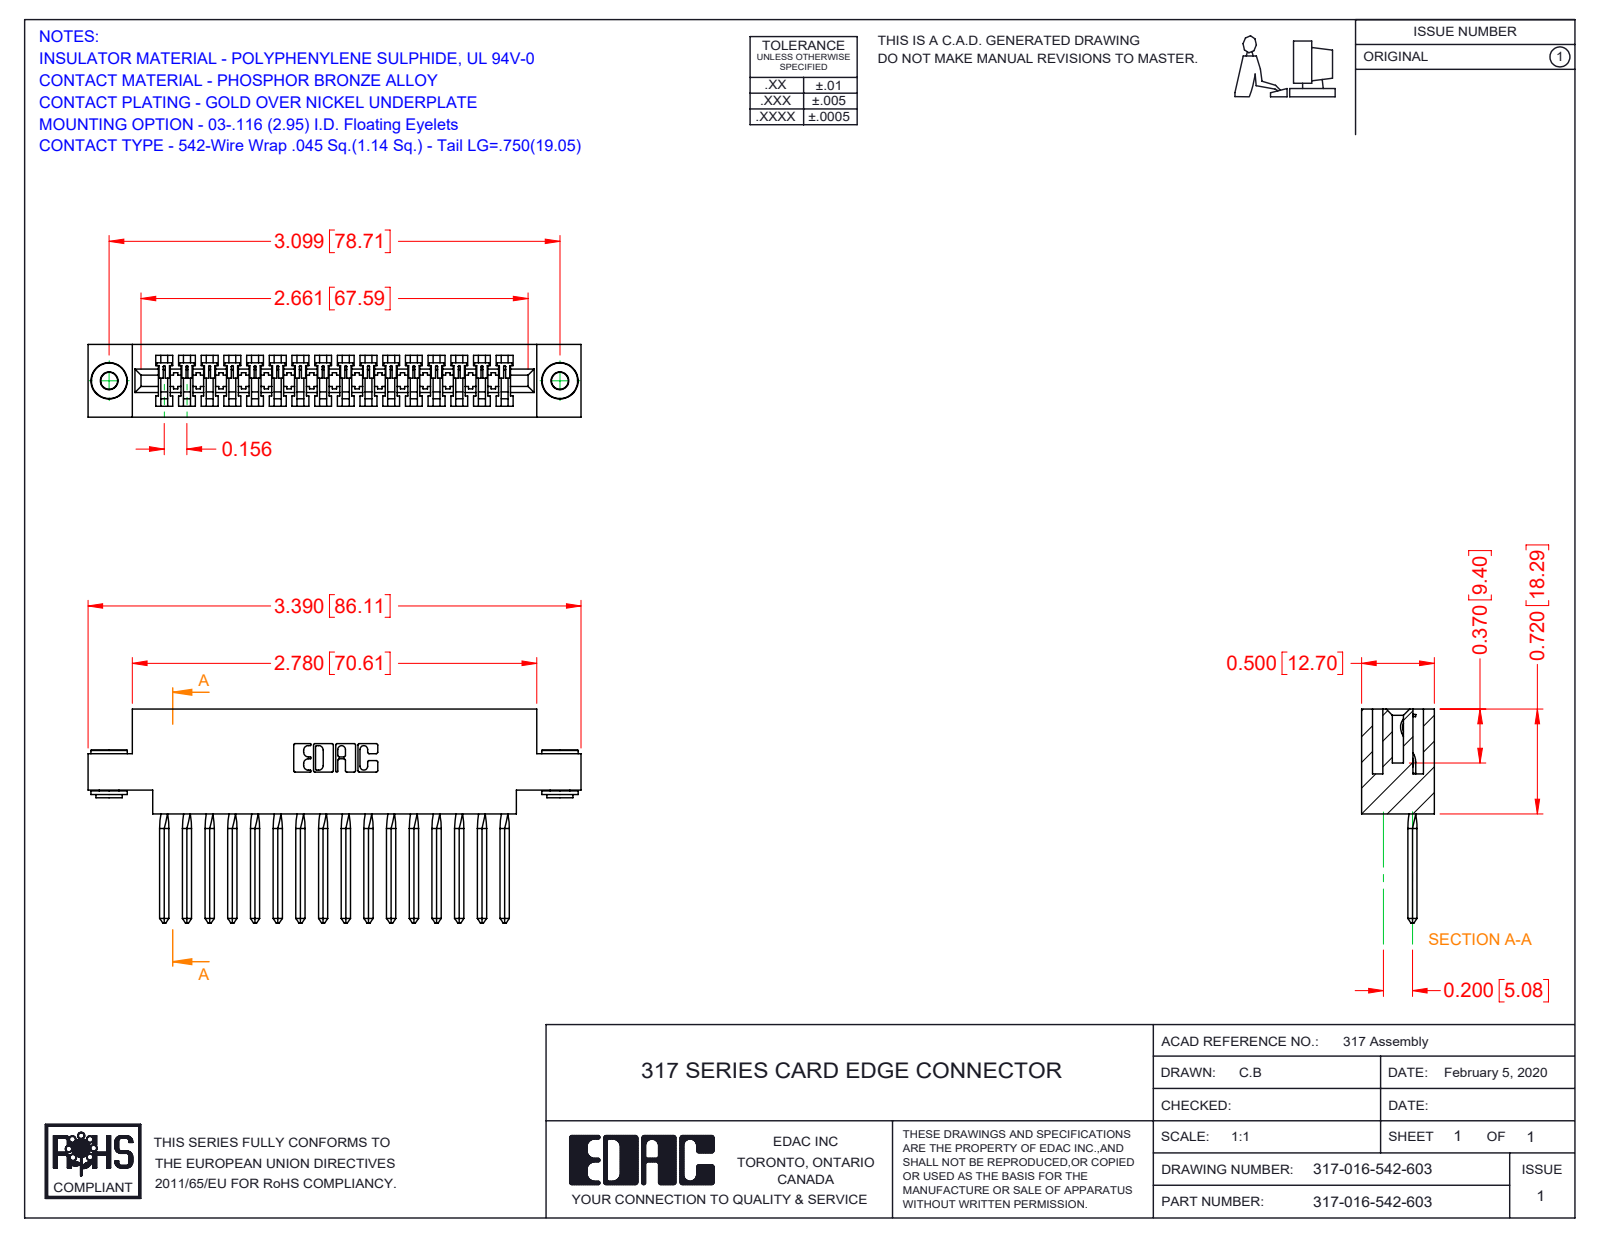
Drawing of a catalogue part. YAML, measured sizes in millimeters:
part_name: "317-290-003_542; 345-250-002_345-250-002-102; 317-016-542-603; 317 Part_.156 Dia - TH"
step_written_by: "SolidWorks 2016 (CONFIG_CONTROL_DESIGN)"
units: millimeters
bodies: {solids: 19, faces: 1340, planar: 1092, cylindrical: 176, other: 72}
overall_size: [86.1, 37.3, 12.7]
volume: 12600
surface_area: 15050
round_holes:
  - {diameter: 2.9, count: 2}
  - {diameter: 4, count: 2}
round_bosses_or_shafts:
  - {diameter: 6.4, count: 2}
  - {diameter: 4.6, count: 2}
  - {diameter: 3.5, count: 2}
partial_cylinders:
  - {radius: 0.2, count: 32}
  - {radius: 0.3, count: 22}
  - {radius: 0.2, count: 6}
  - {radius: 0.8, count: 6}
  - {radius: 0.7, count: 3}
  - {radius: 1.9, count: 1}
  - {radius: 2.3, count: 1}
  - {radius: 2.5, count: 1}
face_to_face_distances: [12.7, 1.9, 10.8, 2.8, 8.9, 1.7, 5.6, 3.5, 18.3, 7.7]
hole_center_spacings: [78.7]
